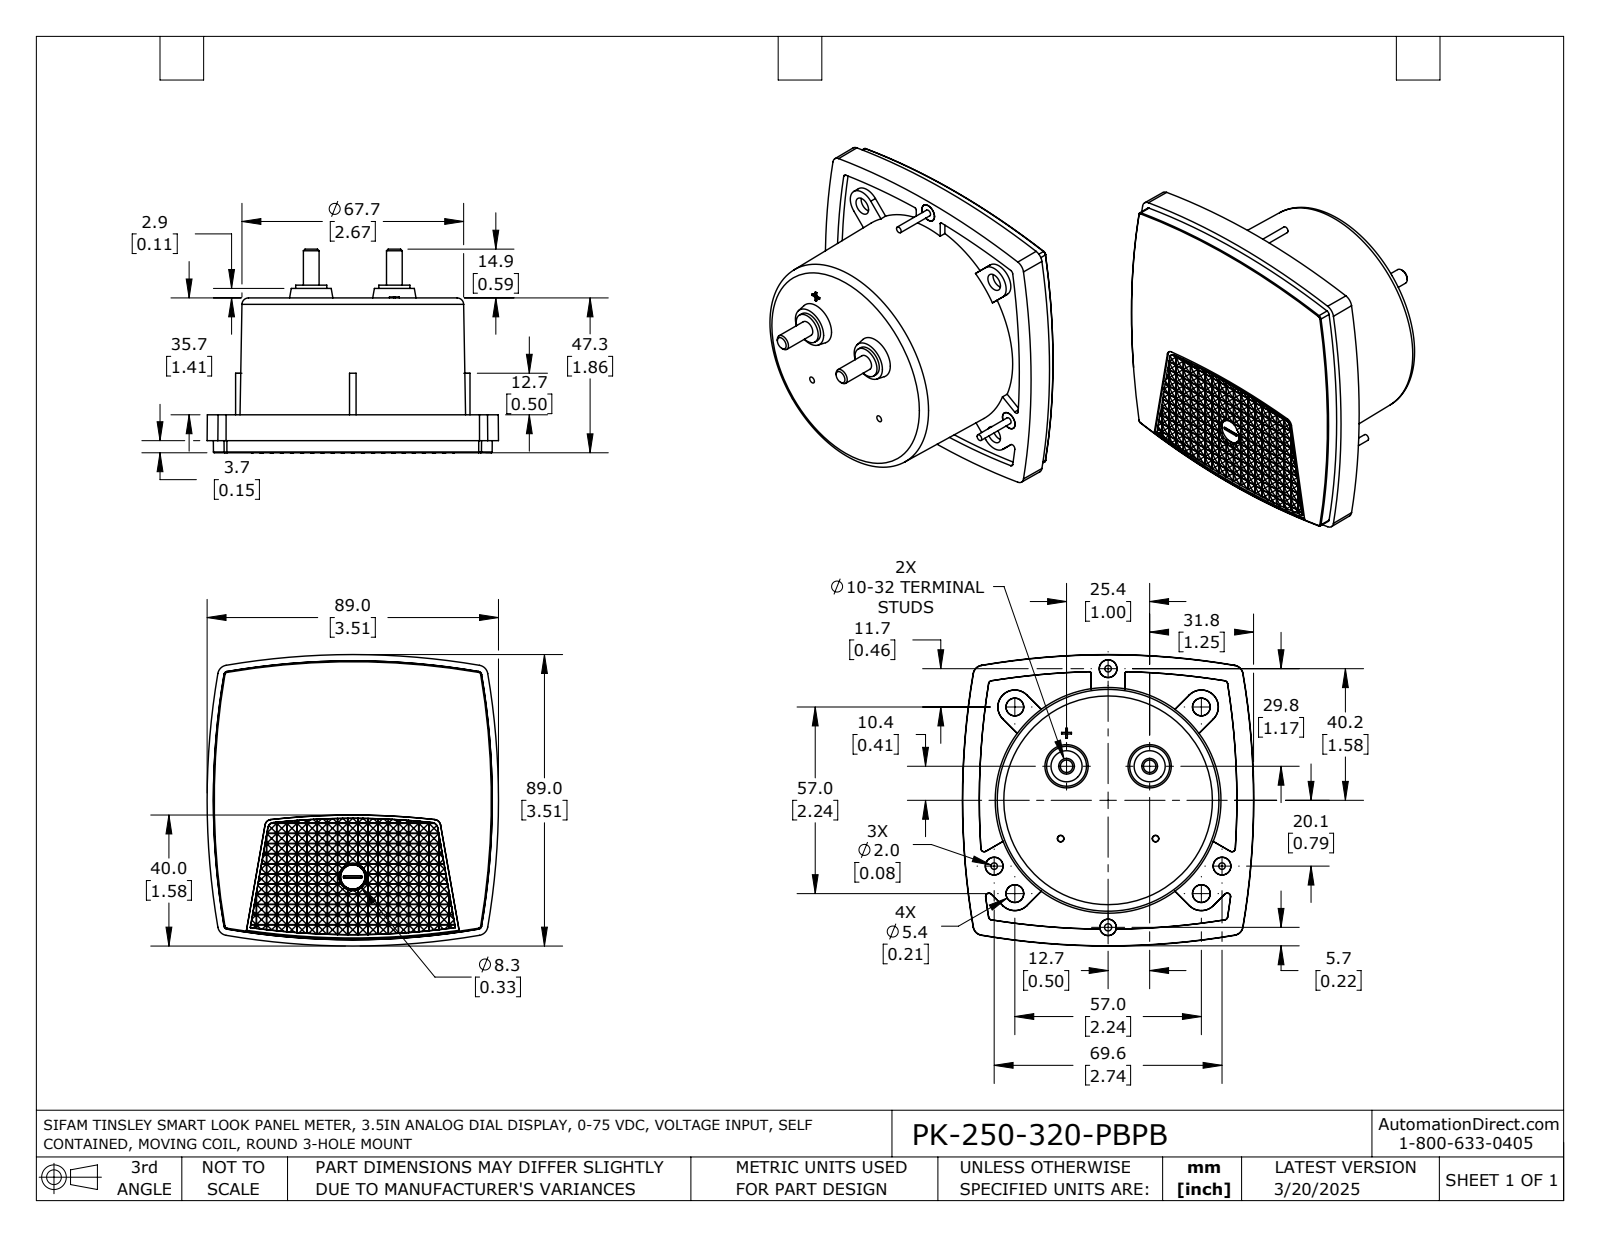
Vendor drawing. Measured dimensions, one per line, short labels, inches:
name: PK-250-320-PBPB
written by: SolidWorks 2021 (AUTOMOTIVE_DESIGN)
unit: in
bodies: 1 solid, 1078 faces (950 planar, 23 cylindrical, 105 other)
size: 3.505 × 3.505 × 2.453
volume: 12.99 in³; area: 44.29 in²
holes: 1× ⌀0.087
bosses: 3× ⌀0.213, 3× ⌀0.079, 2× ⌀0.374, 2× ⌀0.189
rounds: 1× R8.961
face distances: 1.862, 1.406, 0.457, 0.079, 1.484, 0.378, 0.024, 0.096, 0.072, 0.12
